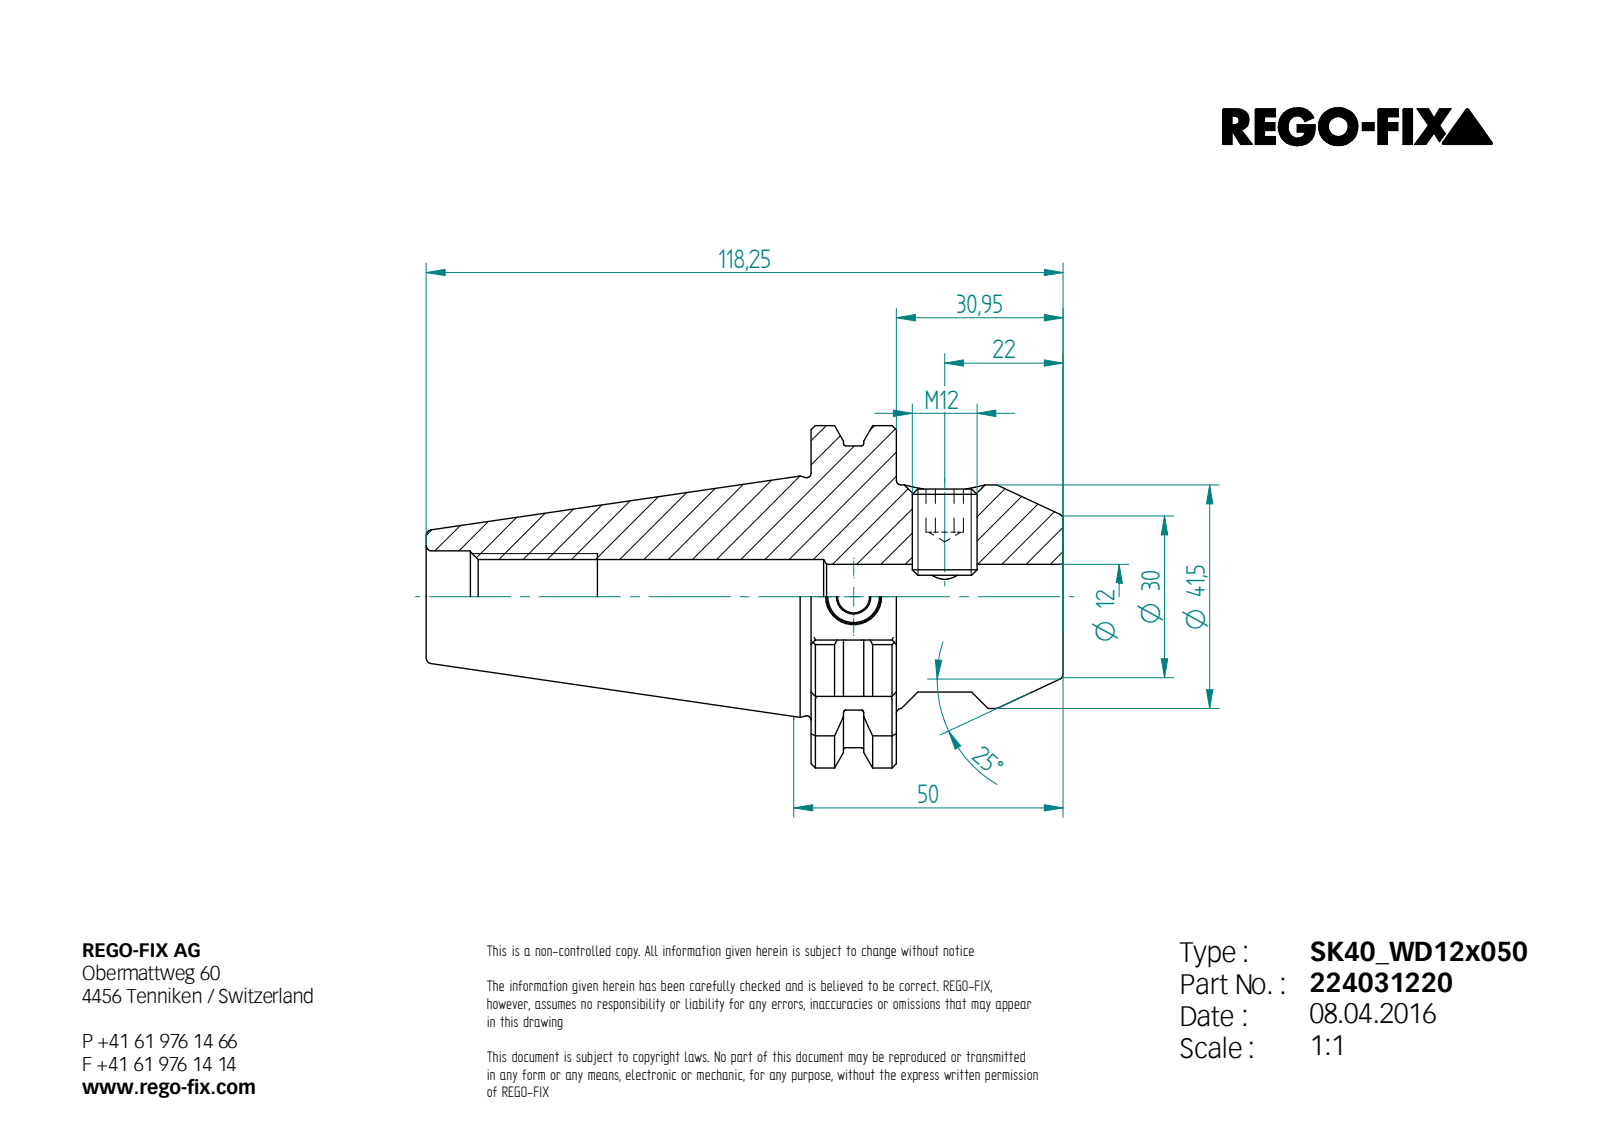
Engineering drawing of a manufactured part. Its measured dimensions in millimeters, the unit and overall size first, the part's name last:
Units: millimetres
Overall size (bounding box): 118.25 × 63.55 × 61.01
Round holes (diameter × count): ⌀6 ×1, ⌀10 ×1, ⌀10.11 ×1, ⌀12 ×1, ⌀13.84 ×1, ⌀17 ×1
Round bosses / shafts (diameter × count): ⌀41.5 ×1, ⌀12 ×1
Partial cylindrical surfaces — rounded edges, fillets, slot ends (radius × count): R0.5 ×13, R28 ×1, R31.77 ×1
Main face-to-face distances: 15.85, 46.8, 30.95, 47.3, 25.75, 9.65, 16.1, 71.45, 87.3, 118.25
Volume: 133 452 mm³ · Surface area: 25 906 mm²
Bodies: 2 solids, 127 faces (58 planar, 31 cylindrical, 38 other)
STEP written by: Unknown (AUTOMOTIVE_DESIGN)
